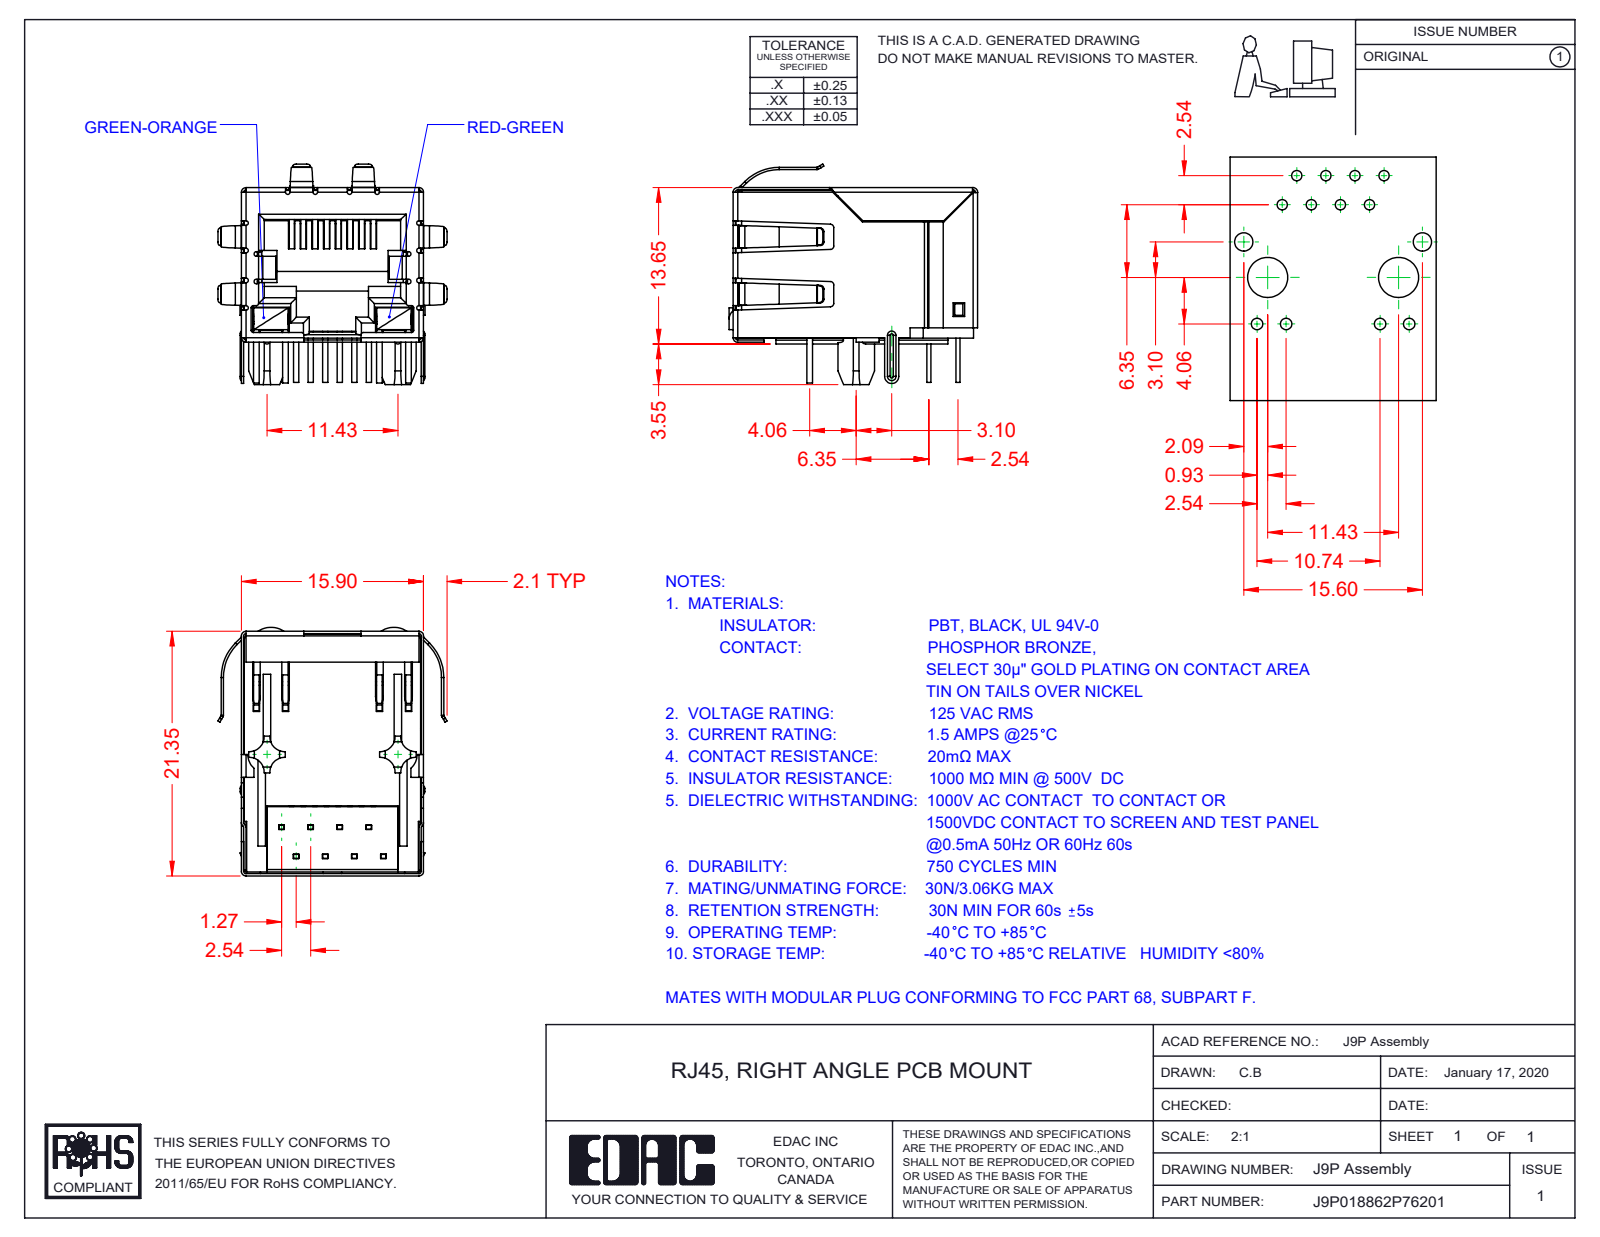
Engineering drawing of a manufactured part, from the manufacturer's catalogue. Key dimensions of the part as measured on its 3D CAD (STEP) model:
Part name (STEP PRODUCT): 9P-LED Contact Lock; 9P-LED Insulator; 9P-LED LED RH_6-Red-Green; J9P018862P76202 (+4 more)
STEP written by: SolidWorks 2016 (CONFIG_CONTROL_DESIGN)
Units: millimetres
Bodies: 13 solids, 1476 faces (1042 planar, 340 cylindrical, 94 other)
Overall size (bounding box): 21.7 × 20 × 19.25
Volume: 2 687 mm³ · Surface area: 7 515 mm²
Partial cylindrical surfaces — rounded edges, fillets, slot ends (radius × count): R0.2 ×39, R0.5 ×22, R0.3 ×20, R0.4 ×16, R1.3 ×8, R0.23 ×5, R0.11 ×4, R0.31 ×4
Main face-to-face distances: 15.45, 15.7, 15.65, 0.35, 0.54, 15.5, 12.36, 0.6, 1.4, 0.59
